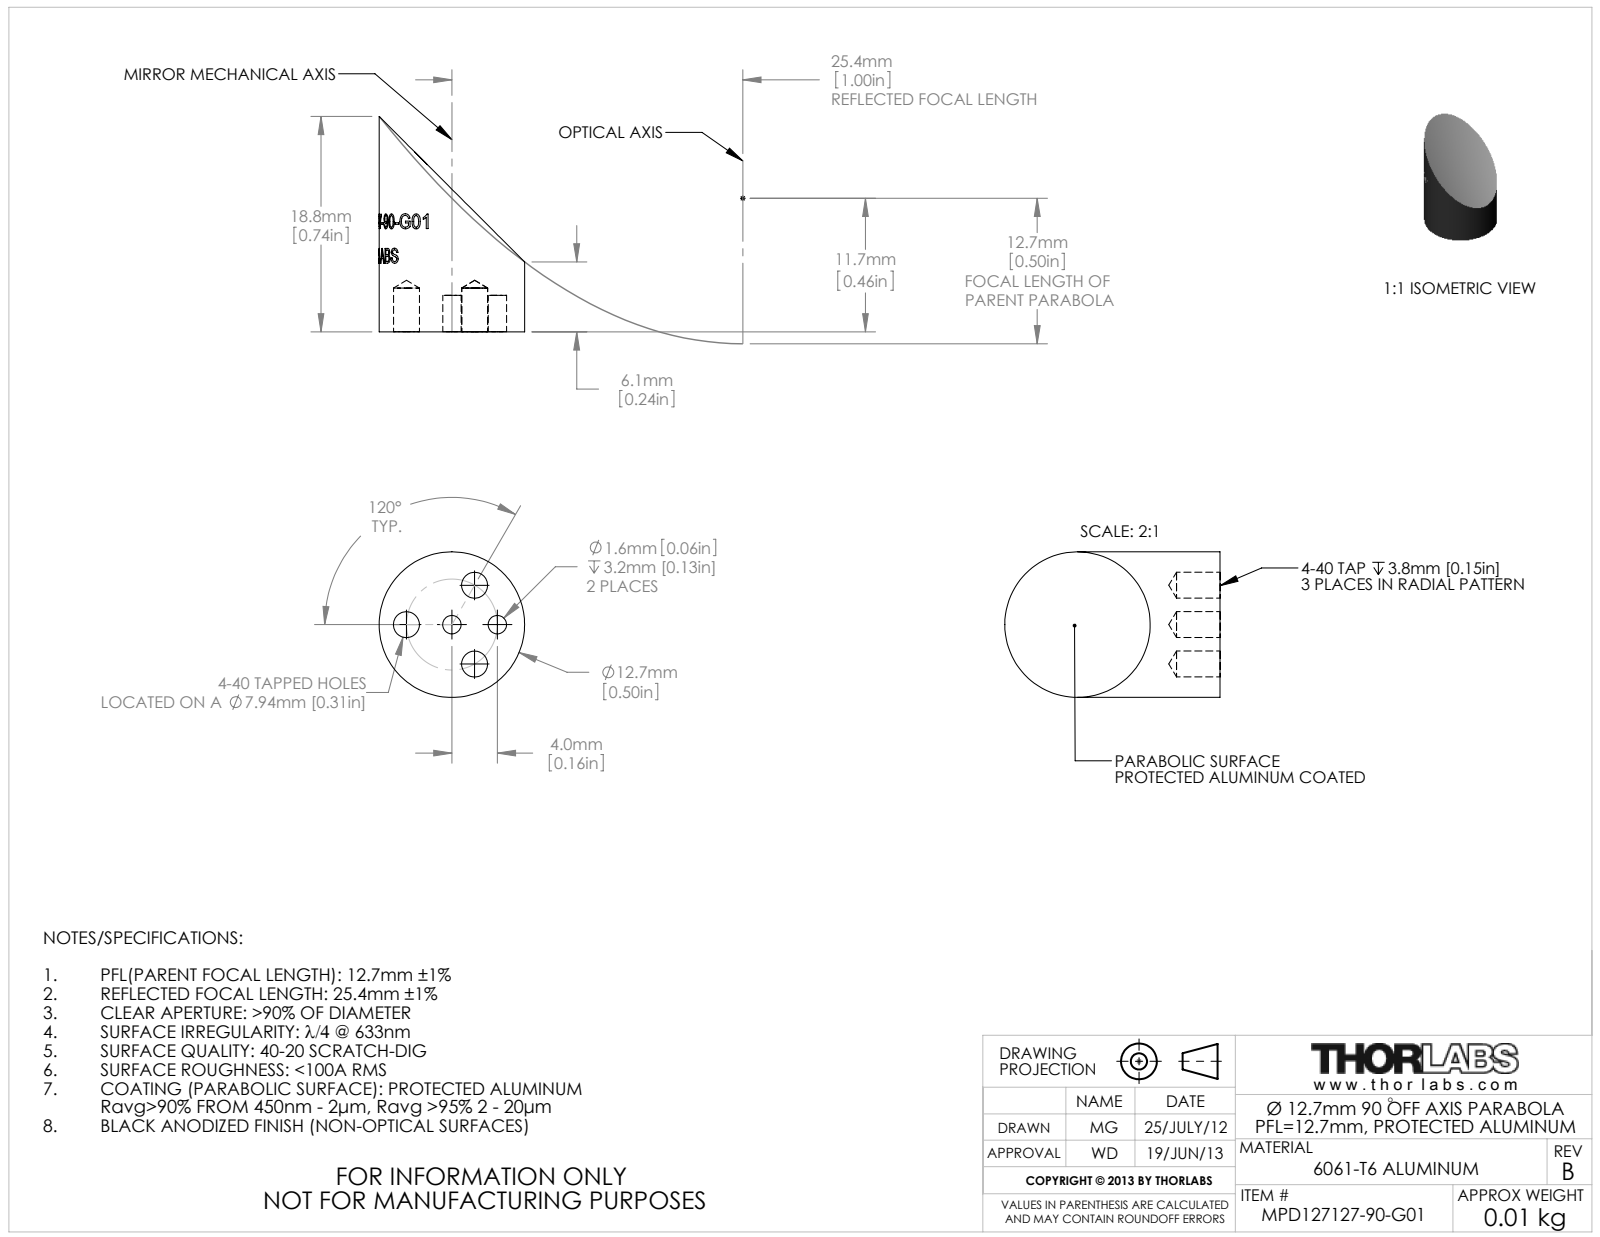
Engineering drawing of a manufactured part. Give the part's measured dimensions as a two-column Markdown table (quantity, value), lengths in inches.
| quantity | value |
| --- | --- |
| part name | 24693-E0W |
| STEP written by | SolidWorks 2012 (CONFIG_CONTROL_DESIGN) |
| units | inches |
| bodies | 1 solid, 57 faces (3 planar, 46 cylindrical, 8 other) |
| overall size | 0.74 × 0.5 × 0.5 |
| volume | 0.089 in³ |
| surface area | 1.42 in² |
| round holes (diameter × count) | 0.089 × 3, 0.063 × 2 |
| round bosses / shafts (diameter × count) | 0.5 × 1 |
| main face-to-face distances | 0.125 |
| hole center spacings | 0.156, 0.27, 0.271, 0.313 |
